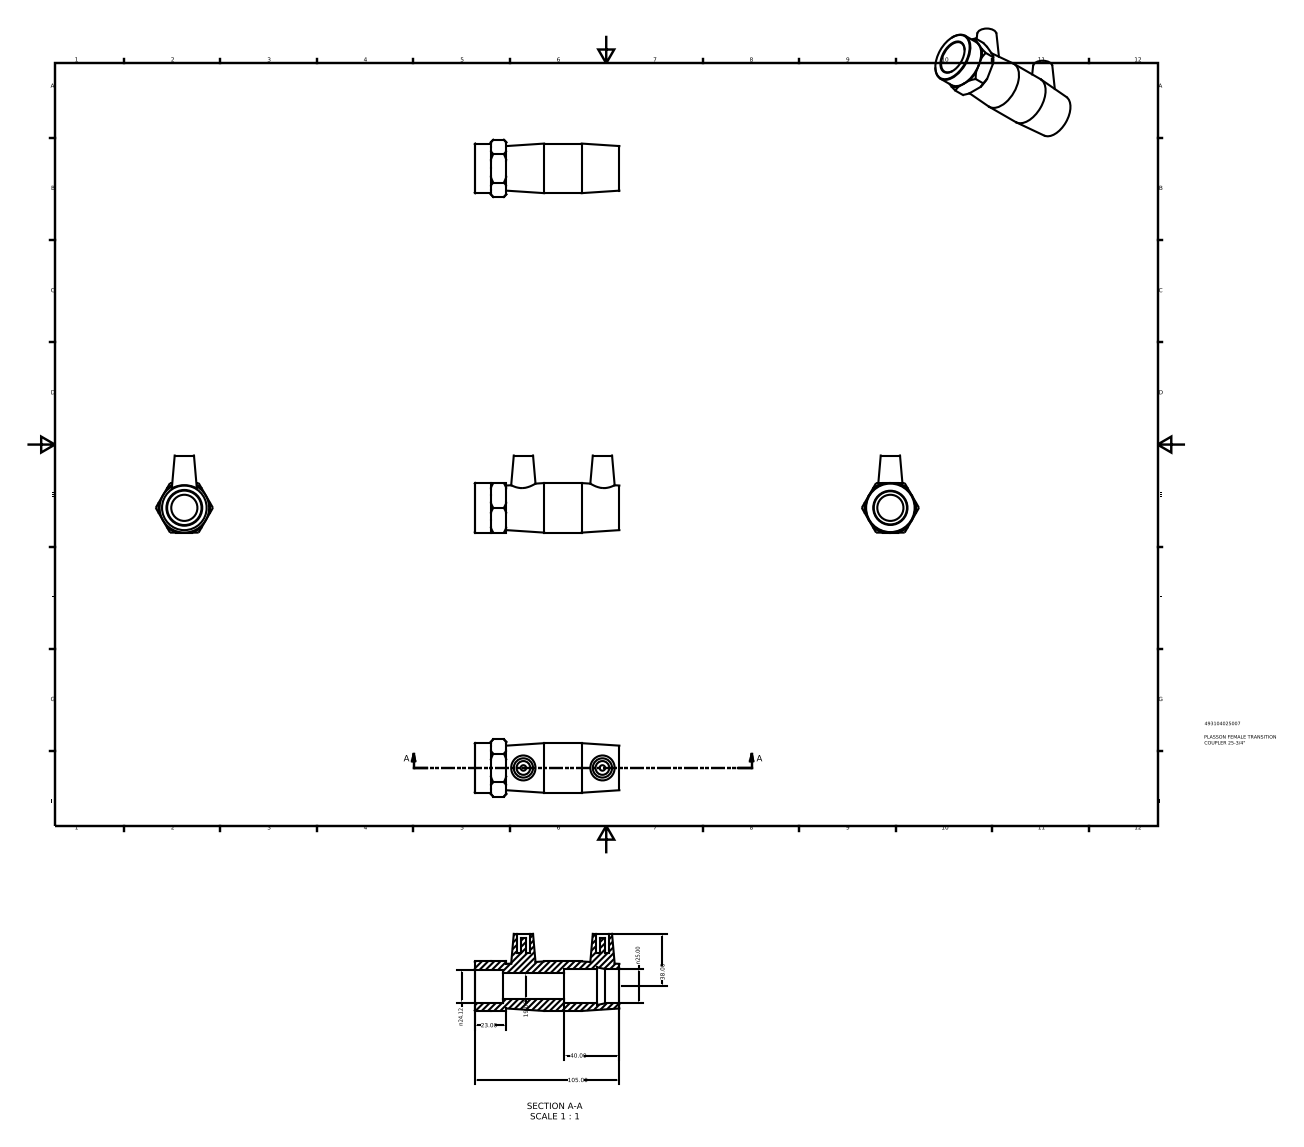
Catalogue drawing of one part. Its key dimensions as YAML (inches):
part_name: "493104025007"
step_written_by: "Autodesk Inventor 2015 (AUTOMOTIVE_DESIGN)"
units: inches
bodies: {solids: 1, faces: 54, planar: 24, cylindrical: 10, other: 20}
overall_size: [4.134, 2.205, 1.637]
volume: 4.114
surface_area: 37.07
round_holes:
  - {diameter: 0.394, count: 2}
  - {diameter: 0.748, count: 1}
  - {diameter: 0.95, count: 1}
  - {diameter: 0.984, count: 1}
round_bosses_or_shafts:
  - {diameter: 0.157, count: 2}
  - {diameter: 1.417, count: 1}
face_to_face_distances: [1.417, 1.654, 4.134, 0.906, 3.228, 2.559, 1.575, 0.815, 0.091, 1.744]
hole_center_spacings: [2.26]
